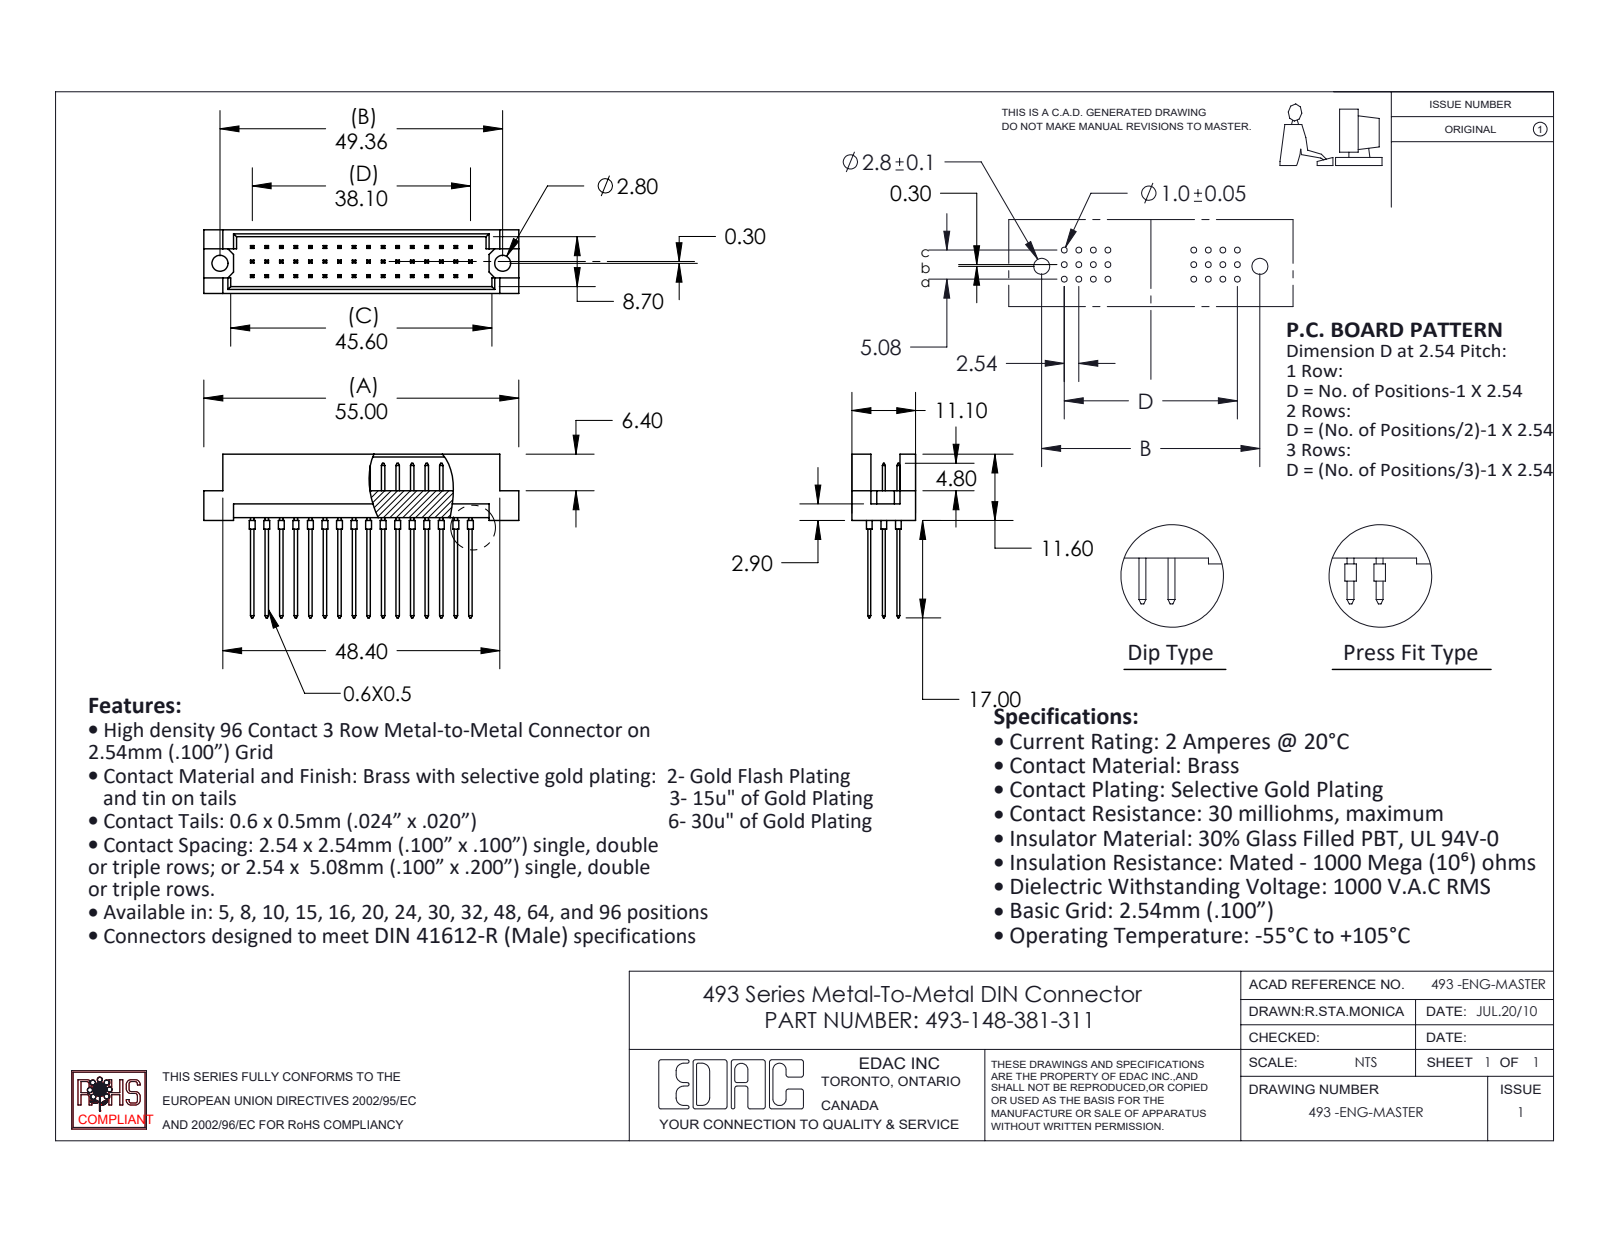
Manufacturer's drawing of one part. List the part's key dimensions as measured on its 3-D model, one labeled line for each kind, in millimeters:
Part name (STEP PRODUCT): 493-290_81; 493-148-381-311; 493 Part_48
STEP written by: SolidWorks 2020 (CONFIG_CONTROL_DESIGN)
Units: millimetres
Bodies: 49 solids, 1300 faces (1200 planar, 100 cylindrical, 0 other)
Overall size (bounding box): 55 × 28.6 × 11.1
Volume: 3 690 mm³ · Surface area: 6 703 mm²
Round holes (diameter × count): ⌀2.8 ×2
Round bosses / shafts (diameter × count): ⌀1 ×48
Main face-to-face distances: 2.54, 5.08, 0.5, 1.2, 9.9, 7.62, 2.76, 5.3, 5.8, 8.34
Hole centre spacings: 49.36
